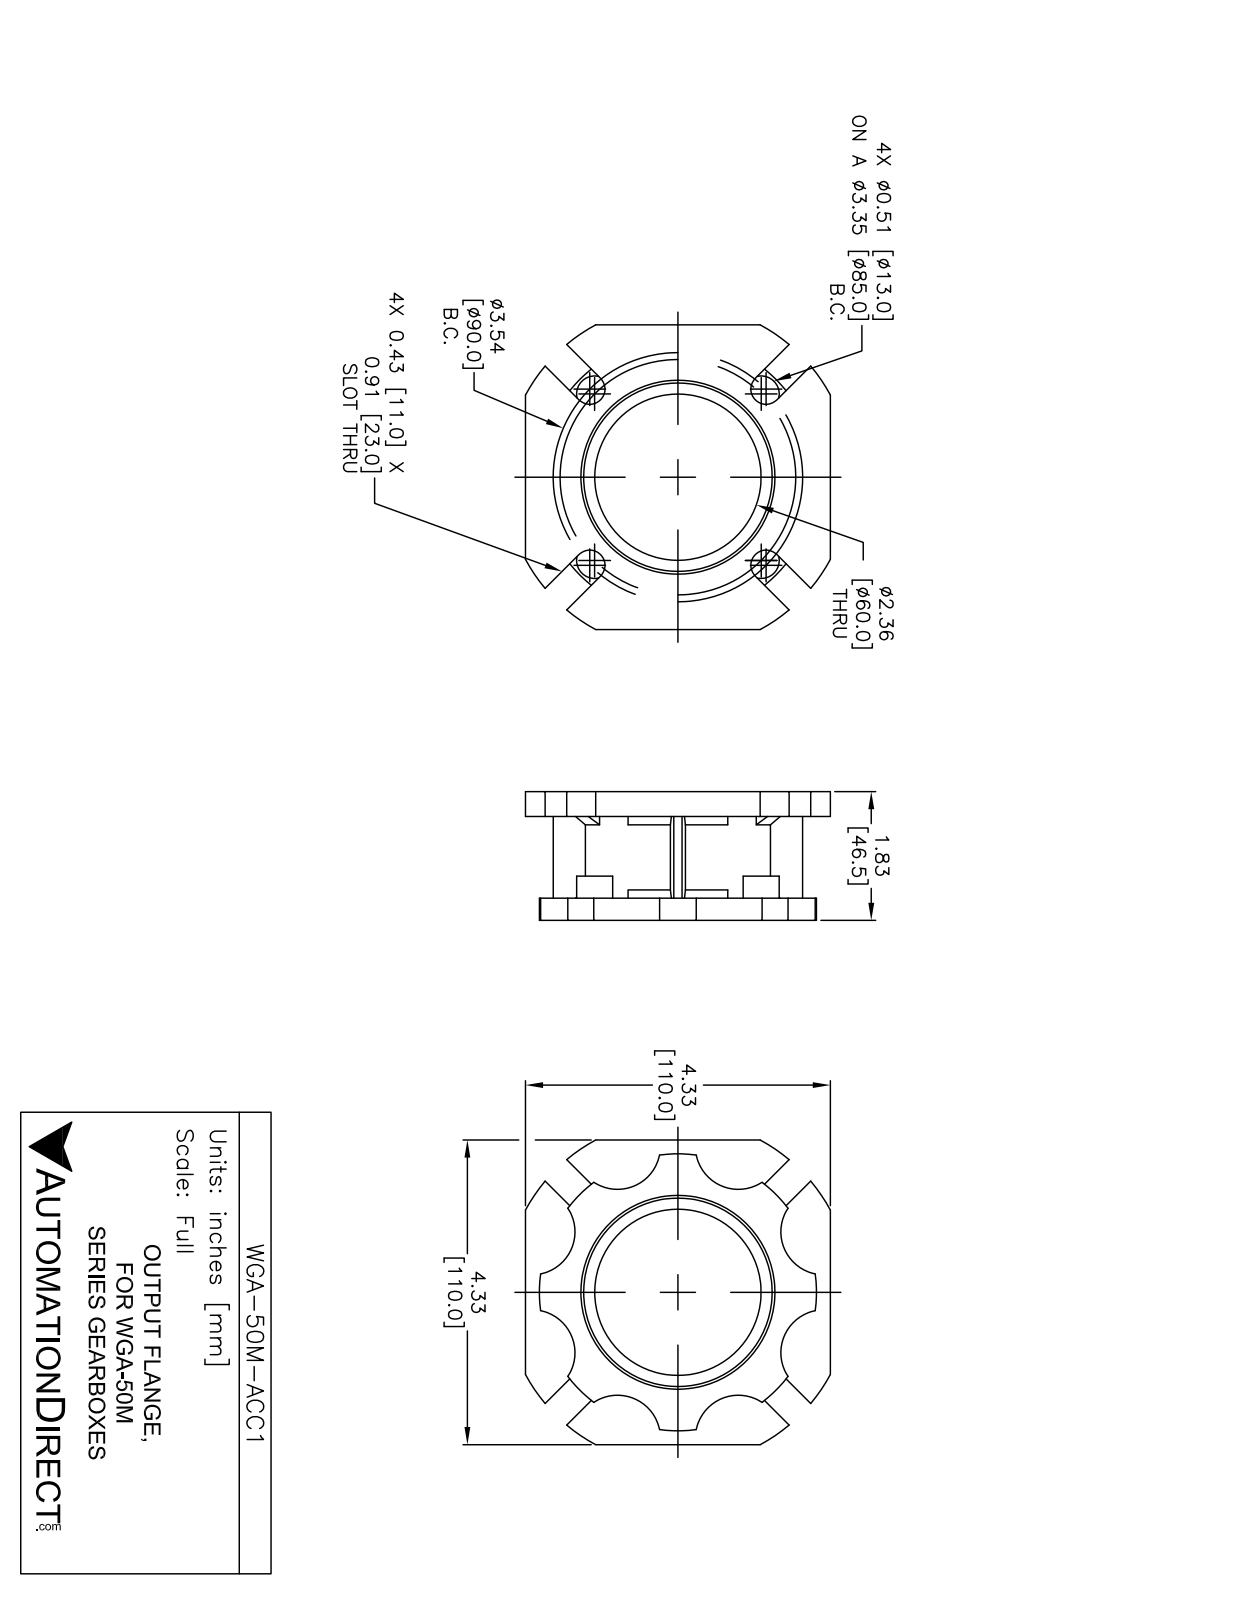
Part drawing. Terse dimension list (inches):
name: WGA-50M-ACC1
written by: SolidWorks 2014 (AUTOMOTIVE_DESIGN)
unit: in
bodies: 1 solid, 137 faces (66 planar, 51 cylindrical, 20 other)
size: 4.331 × 4.331 × 1.831
volume: 7.152 in³; area: 71.42 in²
holes: 1× ⌀2.362, 1× ⌀2.756
bosses: 4× ⌀0.512, 1× ⌀2.638
rounds: 8× R0.61, 4× R0.217, 1× R1.969, 1× R2.461
face distances: 0.354, 1.476, 1.831, 0.315, 1.161, 1.516, 0.49, 4.331, 0.433, 1.201
